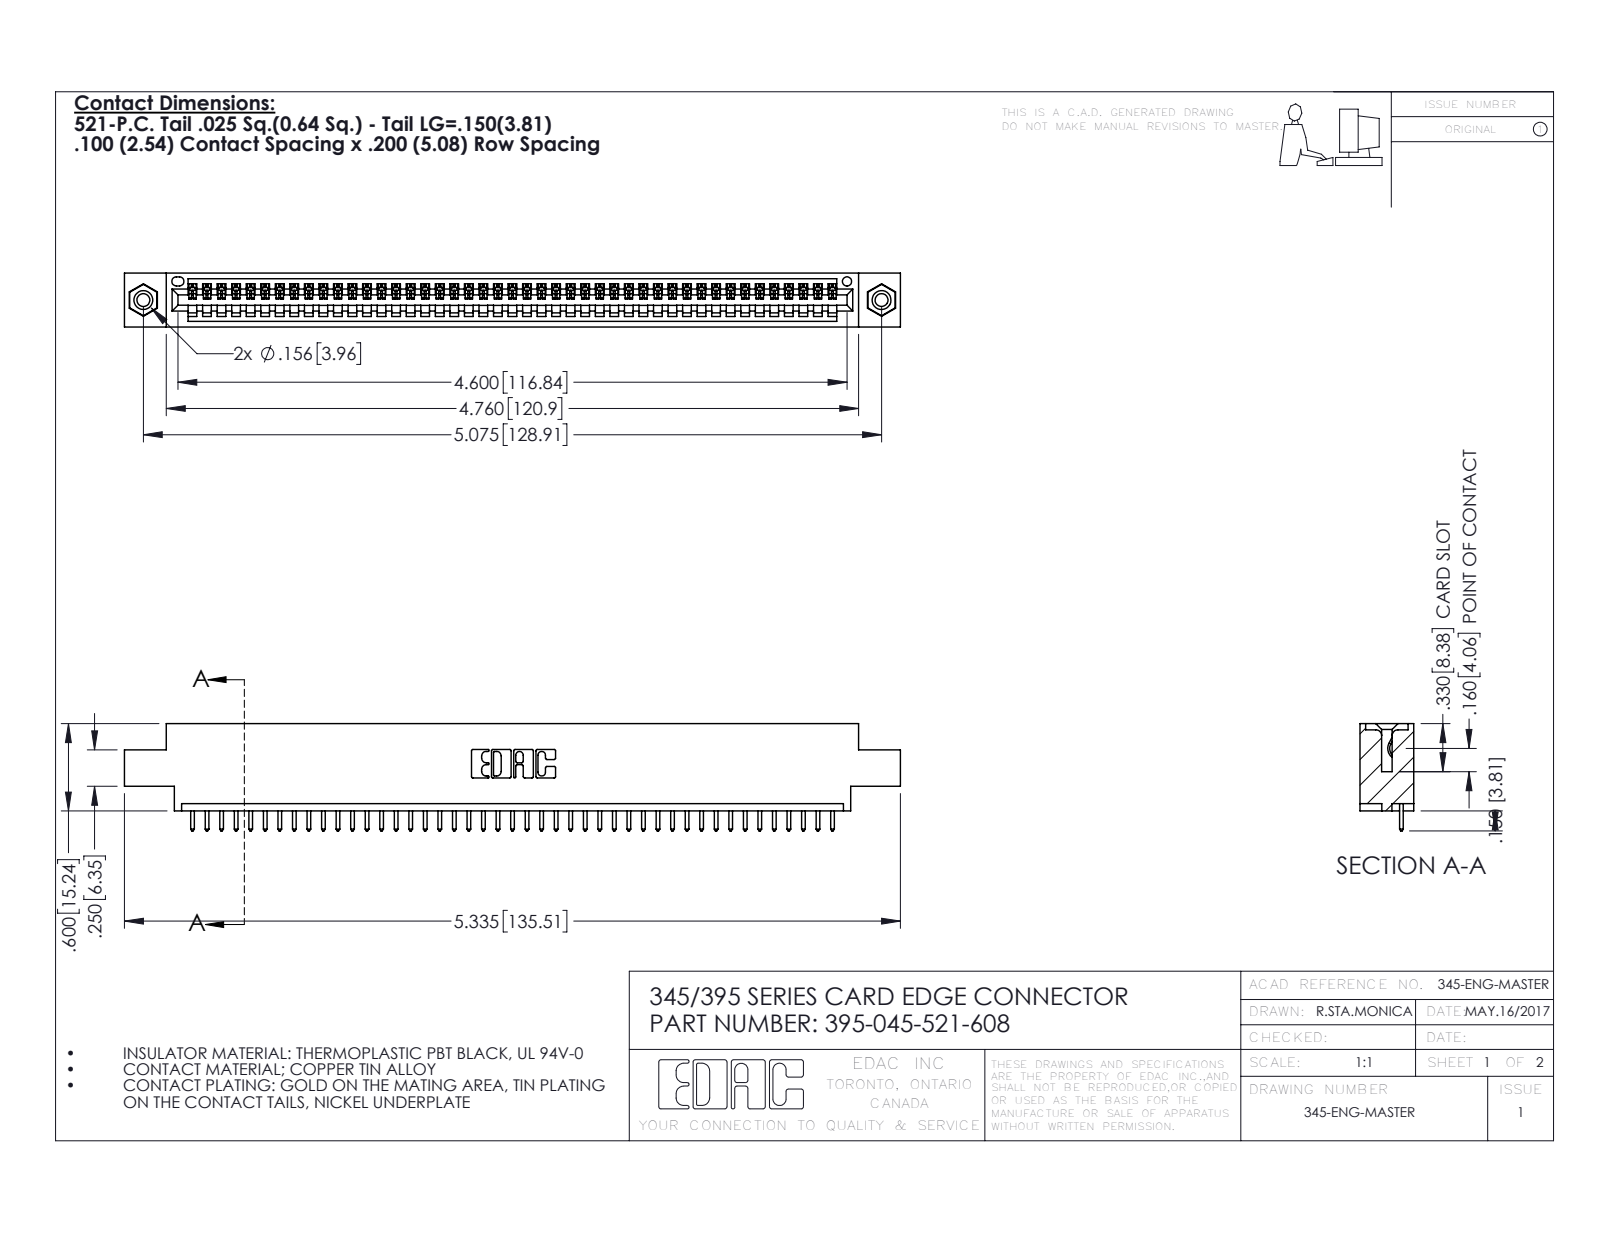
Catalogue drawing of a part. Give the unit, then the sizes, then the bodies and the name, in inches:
Units: inches
Overall size (bounding box): 5.335 × 0.737 × 0.37
Round holes (diameter × count): ⌀0.089 ×2, ⌀0.125 ×2, ⌀0.156 ×2, ⌀0.064 ×1
Round bosses / shafts (diameter × count): ⌀0.155 ×2
Partial cylindrical surfaces — rounded edges, fillets, slot ends (radius × count): R0.006 ×90, R0.01 ×90, R0.01 ×22, R0.007 ×6, R0.031 ×6, R0.026 ×3, R0.031 ×2, R0.04 ×2
Main face-to-face distances: 0.072, 0.298, 0.37, 0.2, 0.098, 0.272, 0.025, 0.225, 0.175, 0.149
Hole centre spacings: 0.27, 4.839, 5.075
Volume: 0.772 in³ · Surface area: 25.56 in²
Bodies: 48 solids, 2800 faces (1916 planar, 868 cylindrical, 16 other)
Part name (STEP PRODUCT): 395-045-521-608; 345-292-001_345-293-121; 345-250-001_345-250-003-102; 345 Part_0.170 Offset - 0.156 Dia-TI
STEP written by: SolidWorks 2016 (CONFIG_CONTROL_DESIGN)
